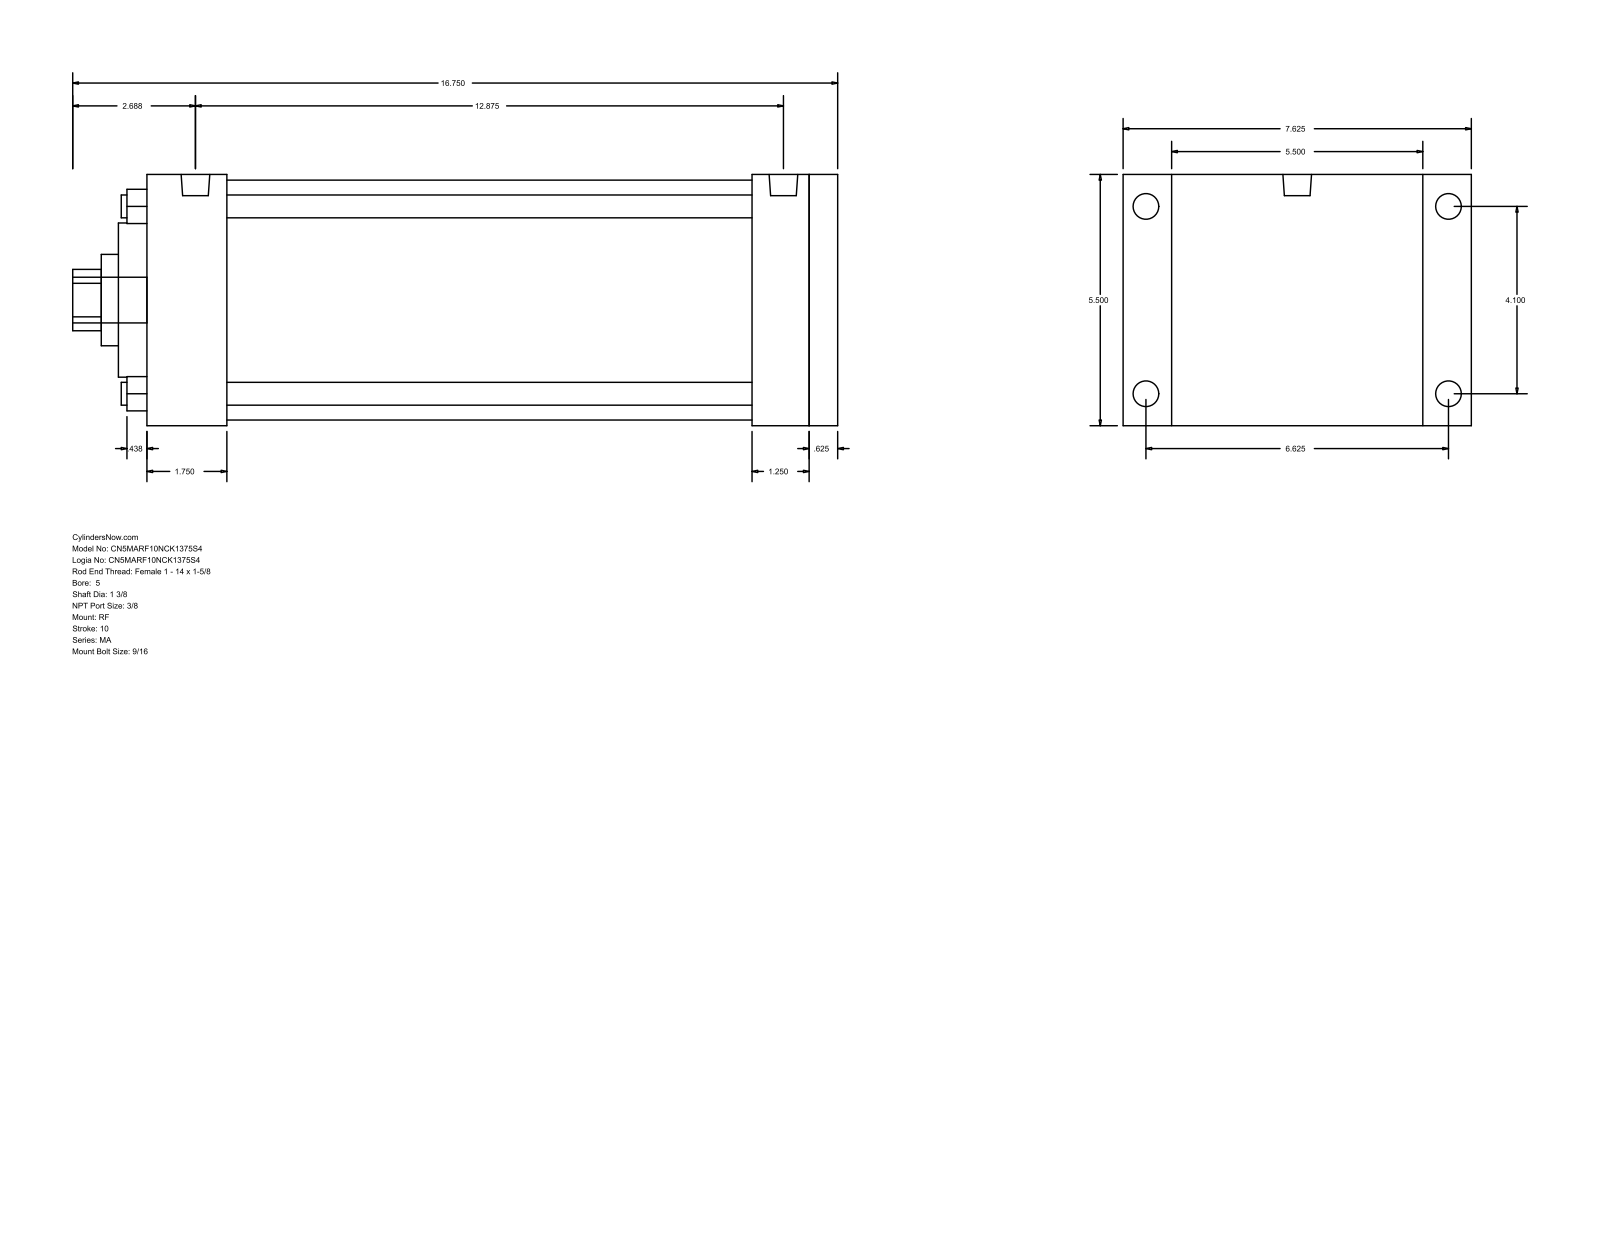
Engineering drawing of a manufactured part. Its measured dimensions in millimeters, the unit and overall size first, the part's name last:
Units: millimetres
Overall size (bounding box): 425.45 × 193.68 × 139.7
Round holes (diameter × count): ⌀12.7 ×4, ⌀34.92 ×1, ⌀50.8 ×1, ⌀85.72 ×1, ⌀133.35 ×1
Round bosses / shafts (diameter × count): ⌀14.29 ×4, ⌀11.11 ×4, ⌀15.93 ×2, ⌀25.4 ×1
Partial cylindrical surfaces — rounded edges, fillets, slot ends (radius × count): R17.06 ×1
Main face-to-face distances: 139.7, 384.18, 15.88, 368.3, 44.45, 323.85, 339.73, 336.55, 292.1, 31.75
Hole centre spacings: 73.64, 104.14, 147.28
Bodies: 0 solids, 94 faces (65 planar, 29 cylindrical, 0 other)
Part name (STEP PRODUCT): MA_RF__0500_1.375
STEP written by: GSSL Pune (CONFIG_CONTROL_DESIGN)
